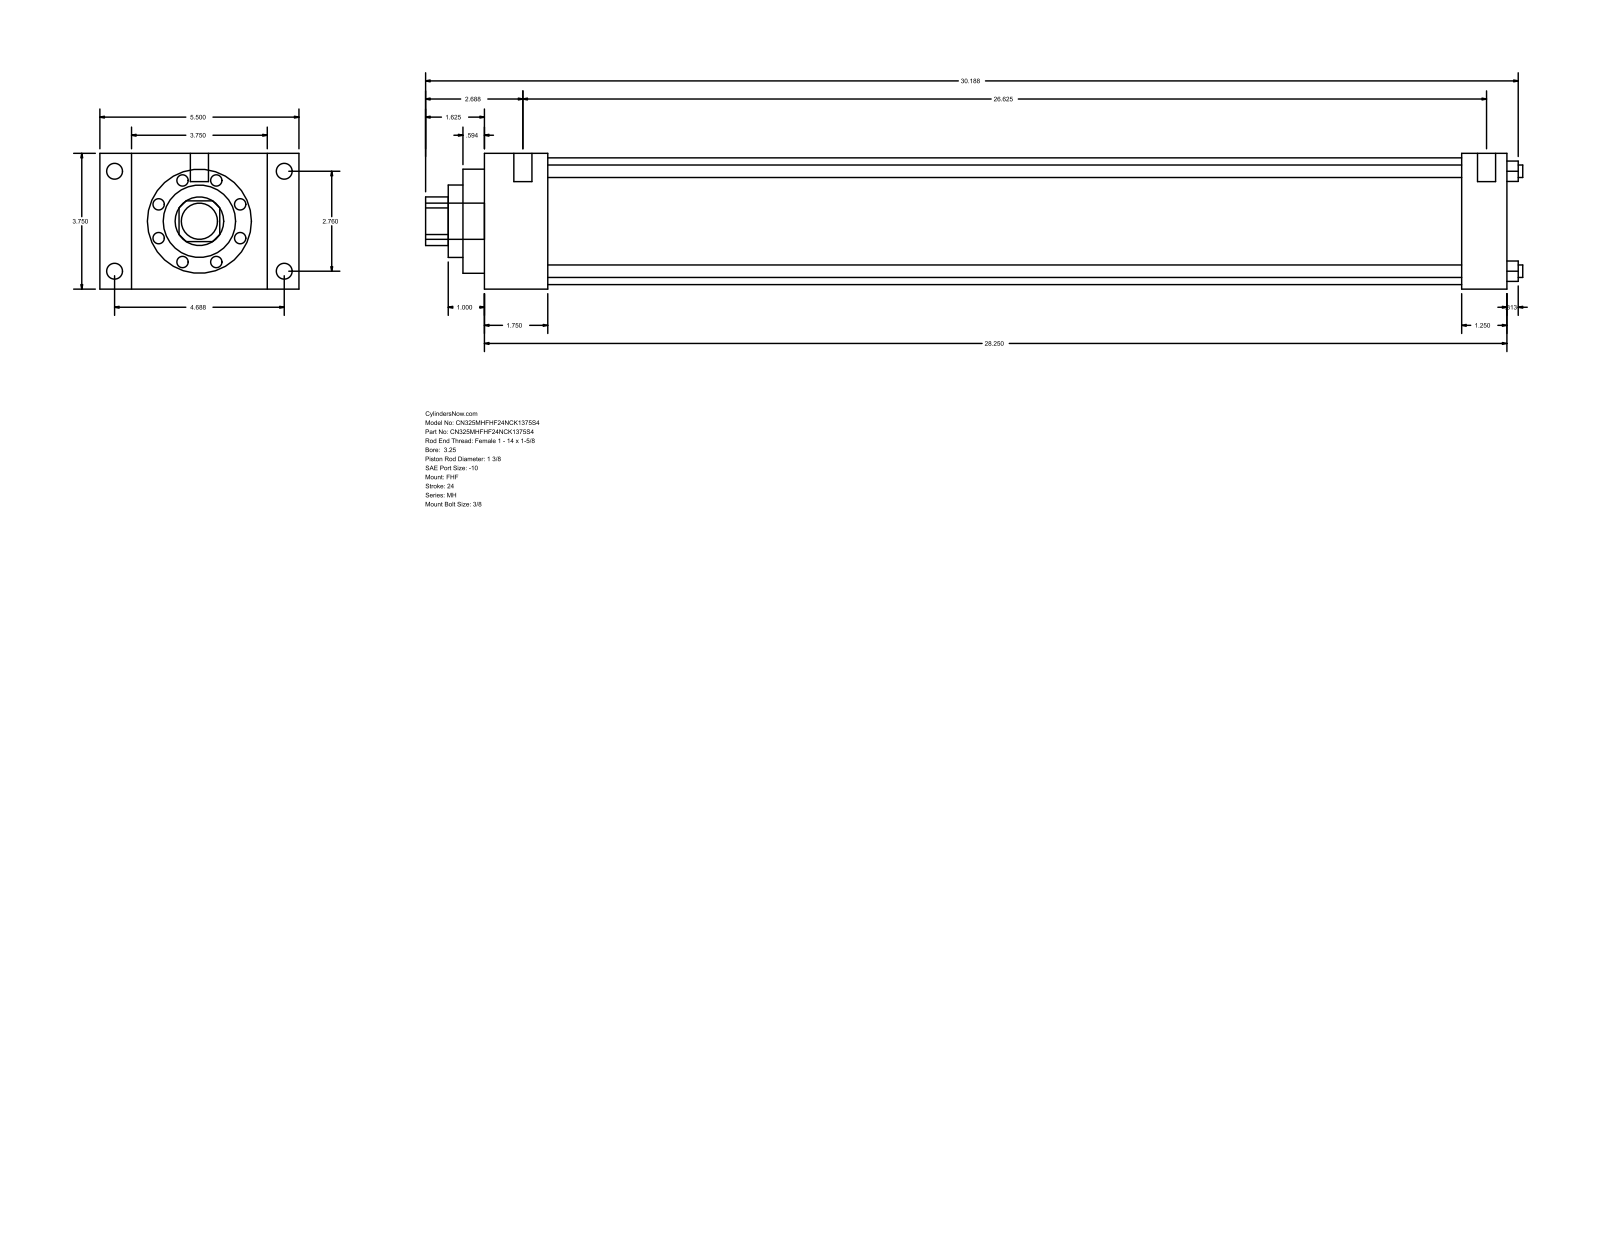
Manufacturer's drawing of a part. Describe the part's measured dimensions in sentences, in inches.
The part is named "MH_FHF__0325_1.375". Its 3-D file was written by "GSSL Pune (CONFIG_CONTROL_DESIGN)". It is 0 solids with 90 faces: 61 planar, 29 cylindrical and 0 other. Overall it measures 30.313 by 5.5 by 3.75 inches. Round holes: 4 of diameter 0.345, 1 of diameter 1.375, 1 of diameter 2, 1 of diameter 2.875, 1 of diameter 3.5. Round bosses or shafts: 4 of diameter 0.438, 4 of diameter 0.219, 2 of diameter 0.5, 1 of diameter 1. Partial cylindrical surfaces (rounded edges, fillets, slot ends): 1 of radius 0.672. The main face-to-face distances are 3.75, 28.25, 1.75, 26.5, 0.875, 4.625, 5.5, 27, 25.25, 1.25. The hole center spacings are 1.952, 2.76, 3.903.
